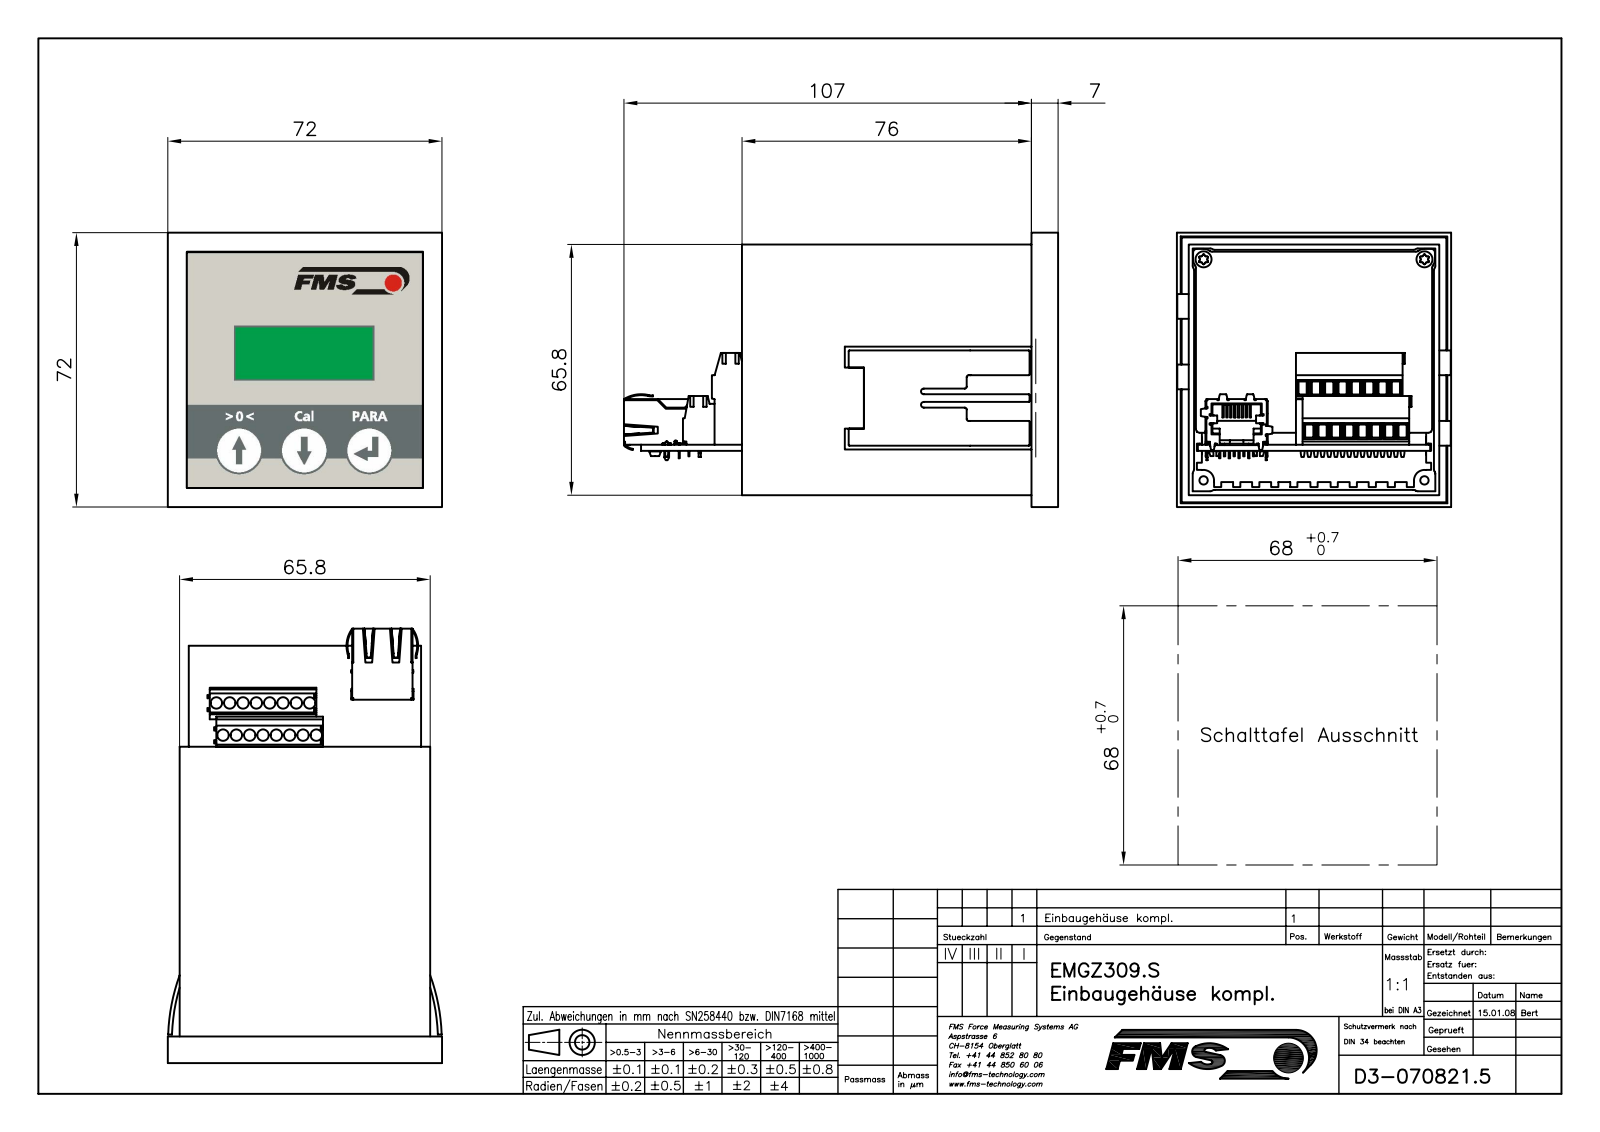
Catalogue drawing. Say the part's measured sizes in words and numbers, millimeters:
The part is named "E0708215; E0708211; TEIL1; TEIL2 (+7 more)". Its 3-D file was written by "Mechanical Desktop 2009 (CONFIG_CONTROL_DESIGN)". It is 13 solids with 1531 faces: 1216 planar, 251 cylindrical and 64 other. Overall it measures 114 by 72 by 72 millimeters. Its volume is 91 584 cubic millimeters and its surface area 96 034 square millimeters. Round holes: 16 of diameter 3, 8 of diameter 2.2, 4 of diameter 1, 2 of diameter 2.5. Round bosses or shafts: 2 of diameter 4.2, 2 of diameter 2.67. Partial cylindrical surfaces (rounded edges, fillets, slot ends): 24 of radius 0.25, 24 of radius 1, 20 of radius 0.2, 19 of radius 0.25, 10 of radius 0.5, 4 of radius 0.1, 4 of radius 0.36, 4 of radius 0.75. The main face-to-face distances are 1, 65.8, 3.45, 62.35, 2.15, 63.65, 1.3, 60.2, 1.6, 1.5. The hole center spacings are 8.63, 3.5, 9.95, 7, 12.16, 10.5, 14.88, 14.
